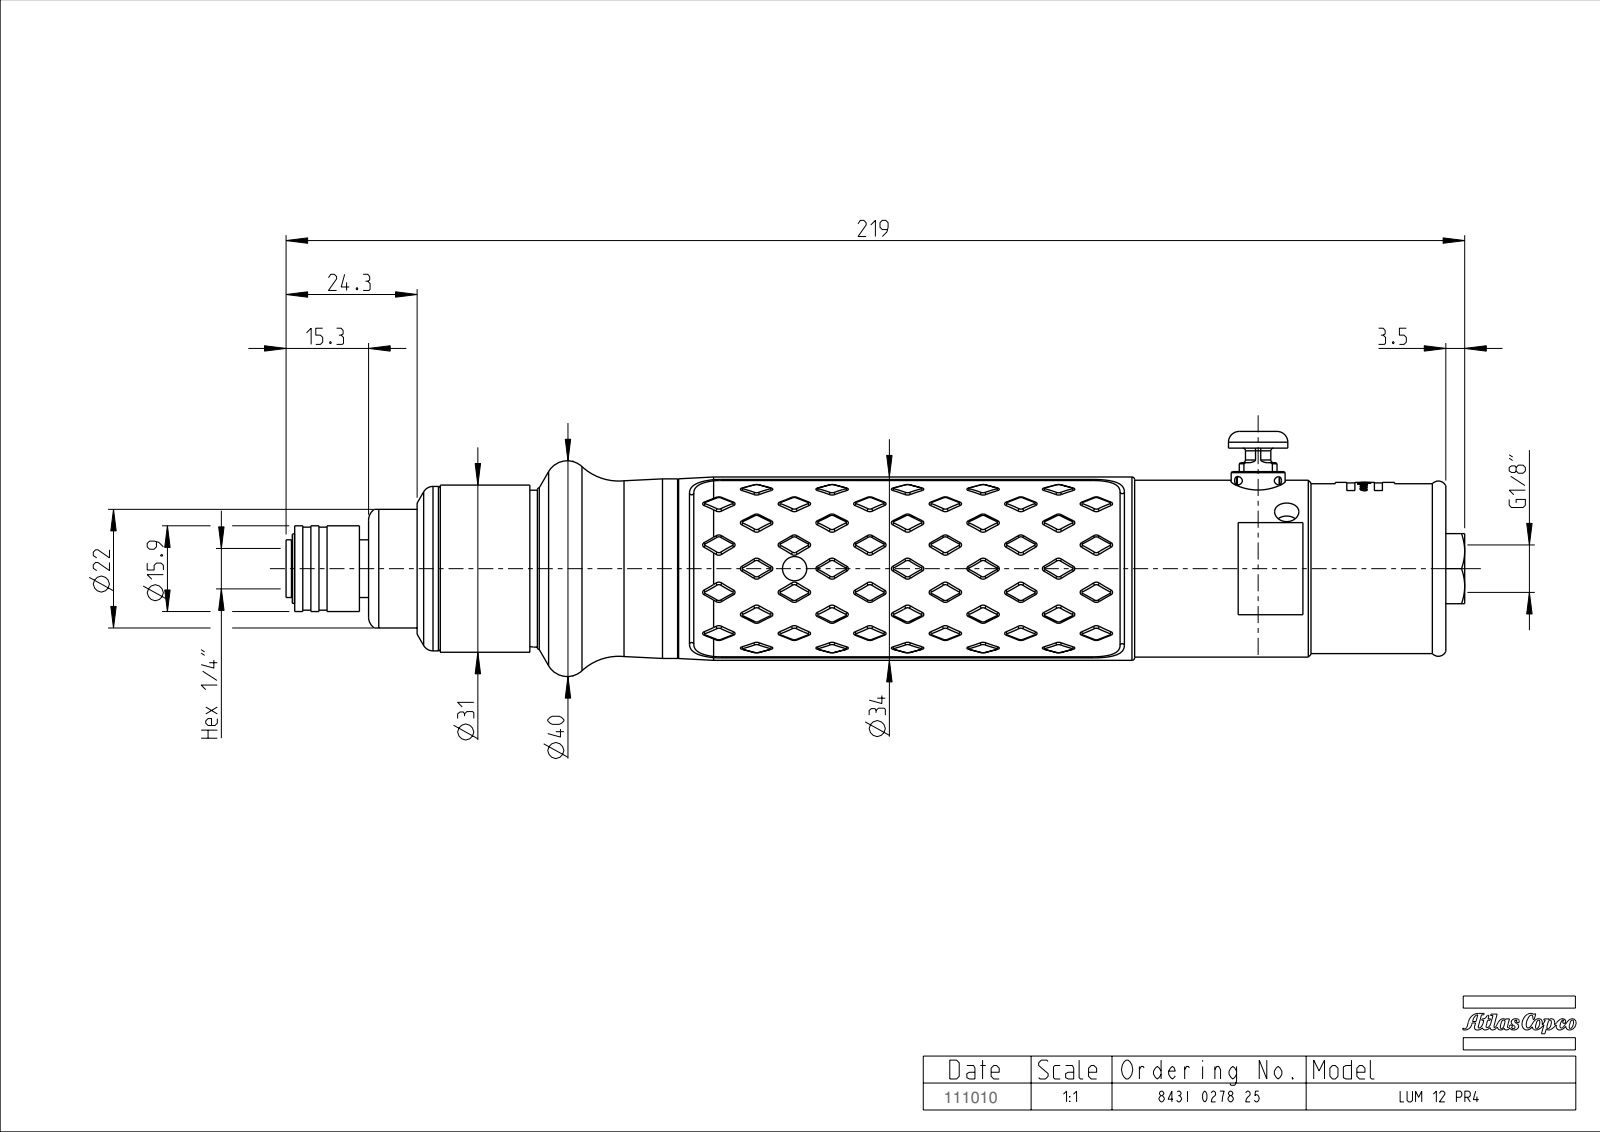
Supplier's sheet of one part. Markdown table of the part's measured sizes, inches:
| quantity | value |
| --- | --- |
| part name | TMP113530_SW |
| STEP written by | PRO/ENGINEER BY PARAMETRIC TECHNOLOGY CORPORATION, 2008310 (CONFIG_CONTROL_DESIGN) |
| units | inches |
| bodies | 0 solids, 659 faces (346 planar, 176 cylindrical, 137 other) |
| overall size | 8.604 × 1.789 × 1.575 |
| round holes (diameter × count) | 0.177 × 3, 0.295 × 1, 0.346 × 1 |
| round bosses / shafts (diameter × count) | 1.339 × 1, 1.311 × 1, 1.291 × 1, 1.244 × 1, 1.24 × 1, 1.22 × 1, 1.201 × 1, 1.146 × 1 |
| partial cylindrical surfaces (radius × count) | 0.016 × 2, 0.02 × 2, 0.059 × 2, 0.03 × 1, 0.157 × 1, 0.626 × 1, 0.63 × 1, 0.677 × 1 |
| main face-to-face distances | 0.131, 0.381, 0.25, 0.512, 1.102, 0.128, 1.191, 0.089, 0.177, 0.308 |
